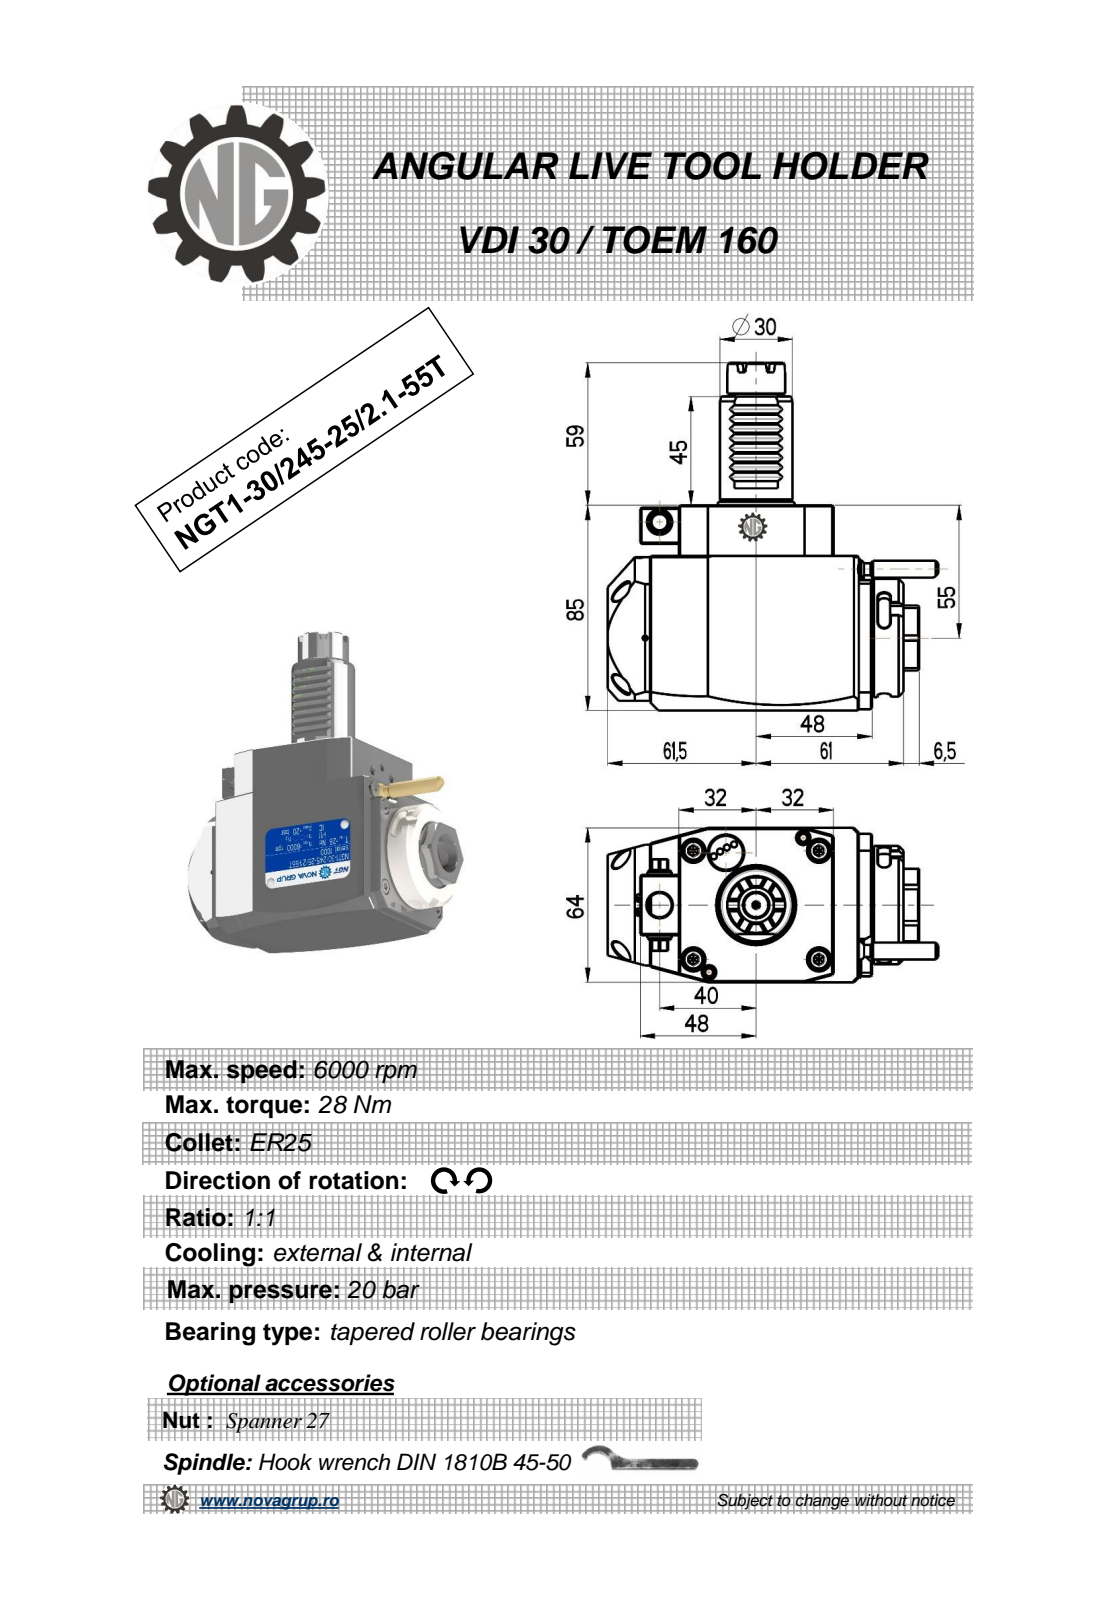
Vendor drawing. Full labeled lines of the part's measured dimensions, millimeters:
Part name (STEP PRODUCT): NGT1_30_245_25_1_1_55T
STEP written by: PRO/ENGINEER BY PARAMETRIC TECHNOLOGY CORPORATION, 2010280 (CONFIG_CONTROL_DESIGN)
Units: millimetres
Bodies: 1 solid, 374 faces (210 planar, 82 cylindrical, 82 other)
Overall size (bounding box): 144 × 136.88 × 64
Volume: 552 438 mm³ · Surface area: 50 140 mm²
Round holes (diameter × count): ⌀2.5 ×1, ⌀3 ×1, ⌀8.5 ×1, ⌀9.5 ×1, ⌀10 ×1, ⌀18 ×1
Round bosses / shafts (diameter × count): ⌀8 ×2, ⌀49 ×1, ⌀42 ×1, ⌀30 ×1, ⌀24 ×1, ⌀17.7 ×1, ⌀15.2 ×1, ⌀10 ×1
Partial cylindrical surfaces — rounded edges, fillets, slot ends (radius × count): R0.3 ×8, R2.5 ×6, R180 ×2, R3.85 ×1, R4.5 ×1, R15 ×1, R21.5 ×1, R33.5 ×1
Main face-to-face distances: 64, 85, 16, 80, 13, 109.5, 21, 122.5, 29, 93.5
Hole centre spacings: 26.17, 34.25, 46.5
